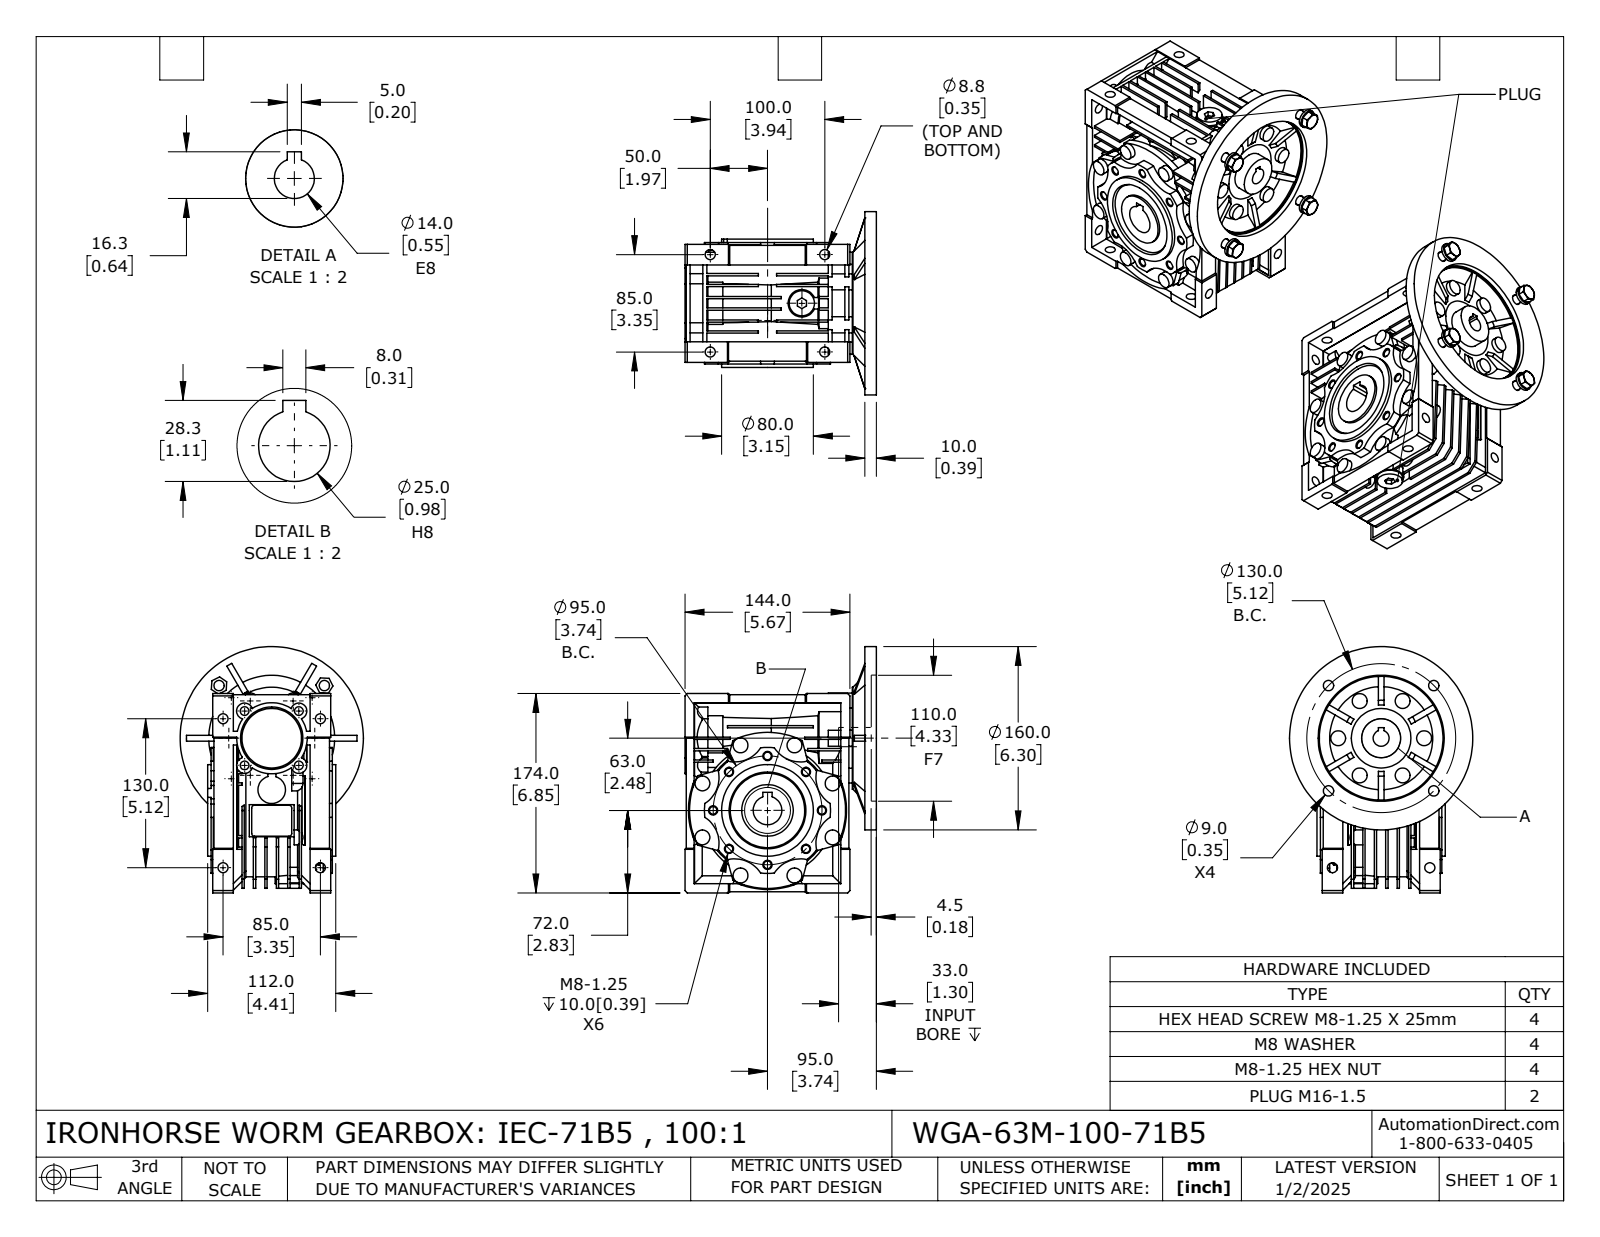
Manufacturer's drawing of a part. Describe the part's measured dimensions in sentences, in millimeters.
The part is named "WGA-63M-100-71B5". Its 3-D file was written by "SolidWorks 2024 (CONFIG_CONTROL_DESIGN)". It is 20 solids with 1516 faces: 887 planar, 379 cylindrical and 250 other. Overall it measures 215 by 182.98 by 160 millimeters. Its volume is 1 919 000 cubic millimeters and its surface area 371 344 square millimeters. Round holes: 8 of diameter 6.65, 8 of diameter 8.78, 4 of diameter 6.8, 4 of diameter 7.56, 4 of diameter 8, 4 of diameter 9, 4 of diameter 9.12, 2 of diameter 14.5, 1 of diameter 14, 1 of diameter 15, 1 of diameter 25, 1 of diameter 34. Round bosses or shafts: 14 of diameter 13, 4 of diameter 16, 3 of diameter 24, 2 of diameter 22, 2 of diameter 15.8, 2 of diameter 13.7, 1 of diameter 160, 1 of diameter 110. Partial cylindrical surfaces (rounded edges, fillets, slot ends): 10 of radius 7, 8 of radius 27, 4 of radius 2.5, 1 of radius 8.35, 1 of radius 29.5, 1 of radius 30.5, 1 of radius 42, 1 of radius 58. The main face-to-face distances are 10, 8, 20, 2, 30, 12, 7, 18, 40, 1. The hole center spacings are 36.36, 47.5, 67.18, 73.12, 87.77, 31.49, 33.5, 47.38.
